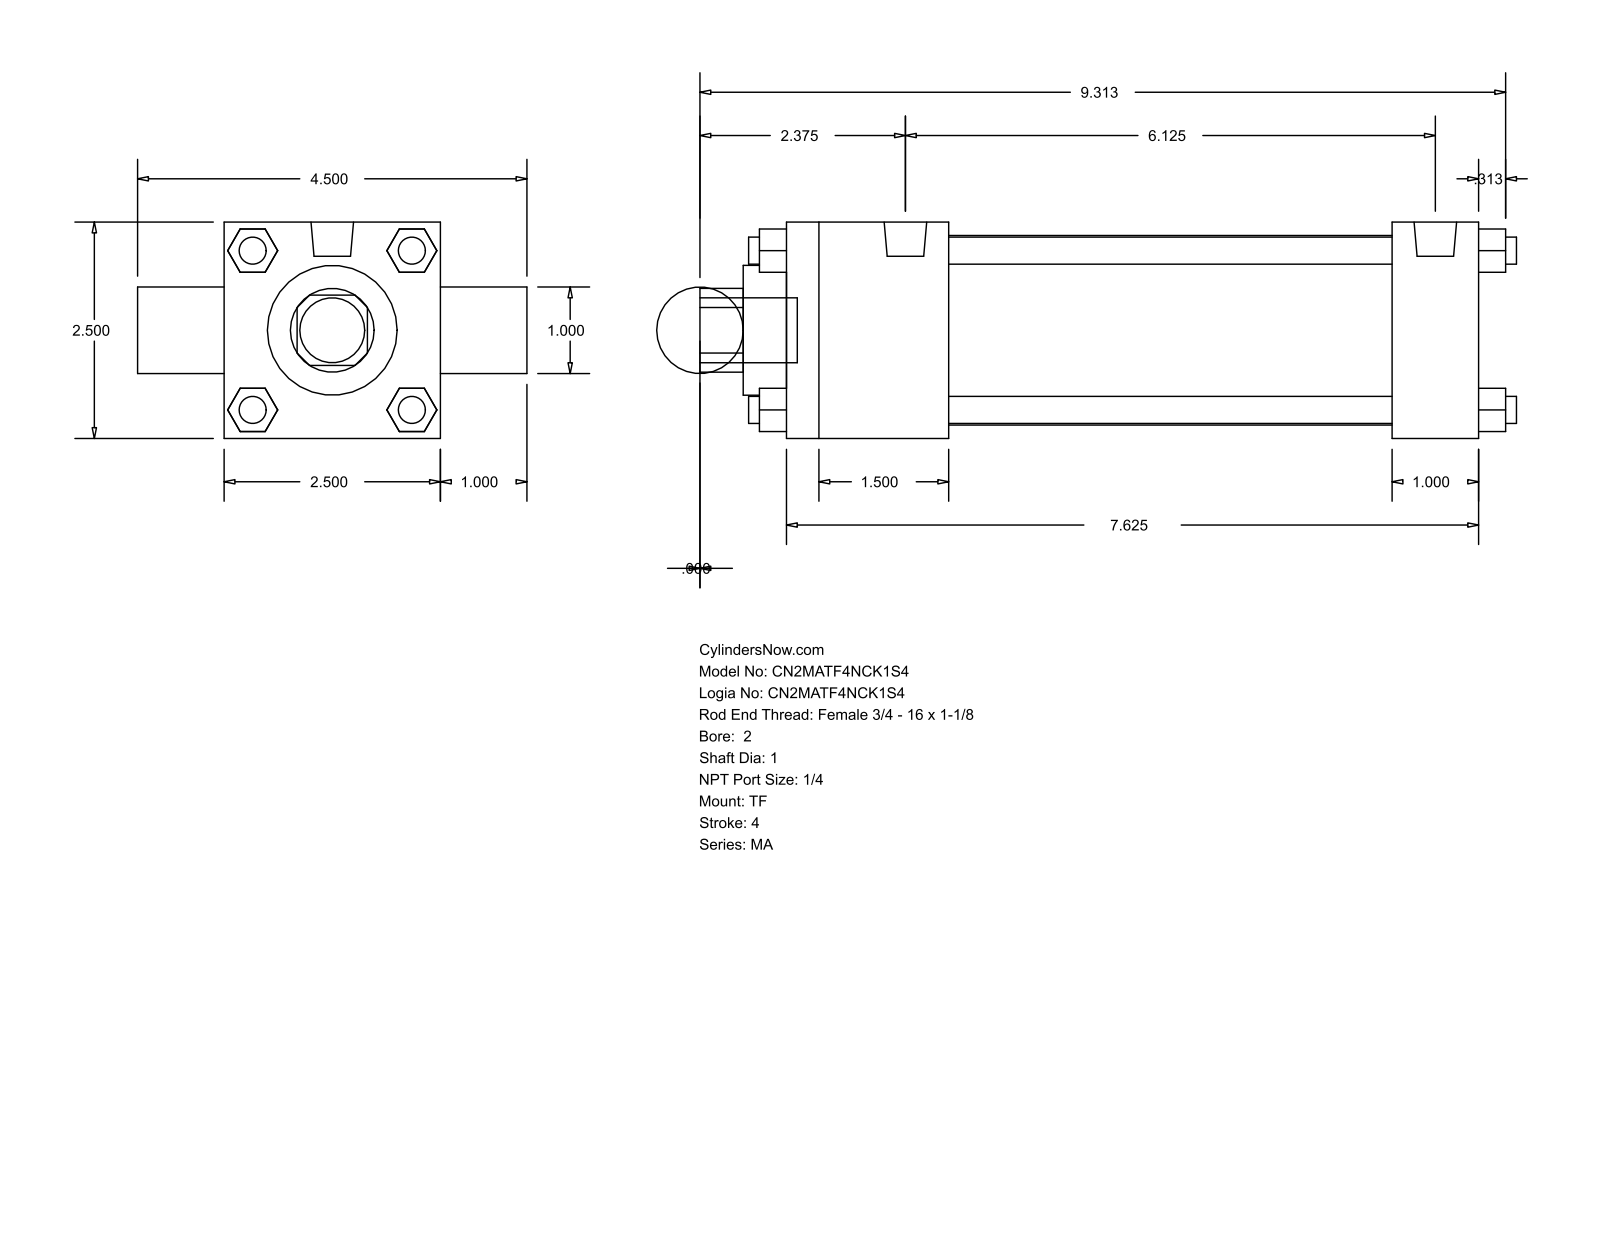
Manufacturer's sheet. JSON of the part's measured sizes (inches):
{"part_name": "MA_TF__0200_1", "step_written_by": "GSSL Pune (CONFIG_CONTROL_DESIGN)", "units": "inches", "bodies": {"solids": 0, "faces": 120, "planar": 92, "cylindrical": 28, "other": 0}, "overall_size": [9.437, 4.5, 2.5], "round_holes": [[1, 2], [1.5, 1], [2.19, 1]], "round_bosses_or_shafts": [[0.313, 7], [0.492, 2], [0.75, 1]], "partial_cylinders_radius": [[0.484, 1]], "face_to_face_distances": [2.5, 1, 8, 0.5, 1.875, 7, 5.125, 6.125, 3.5, 0.92]}
